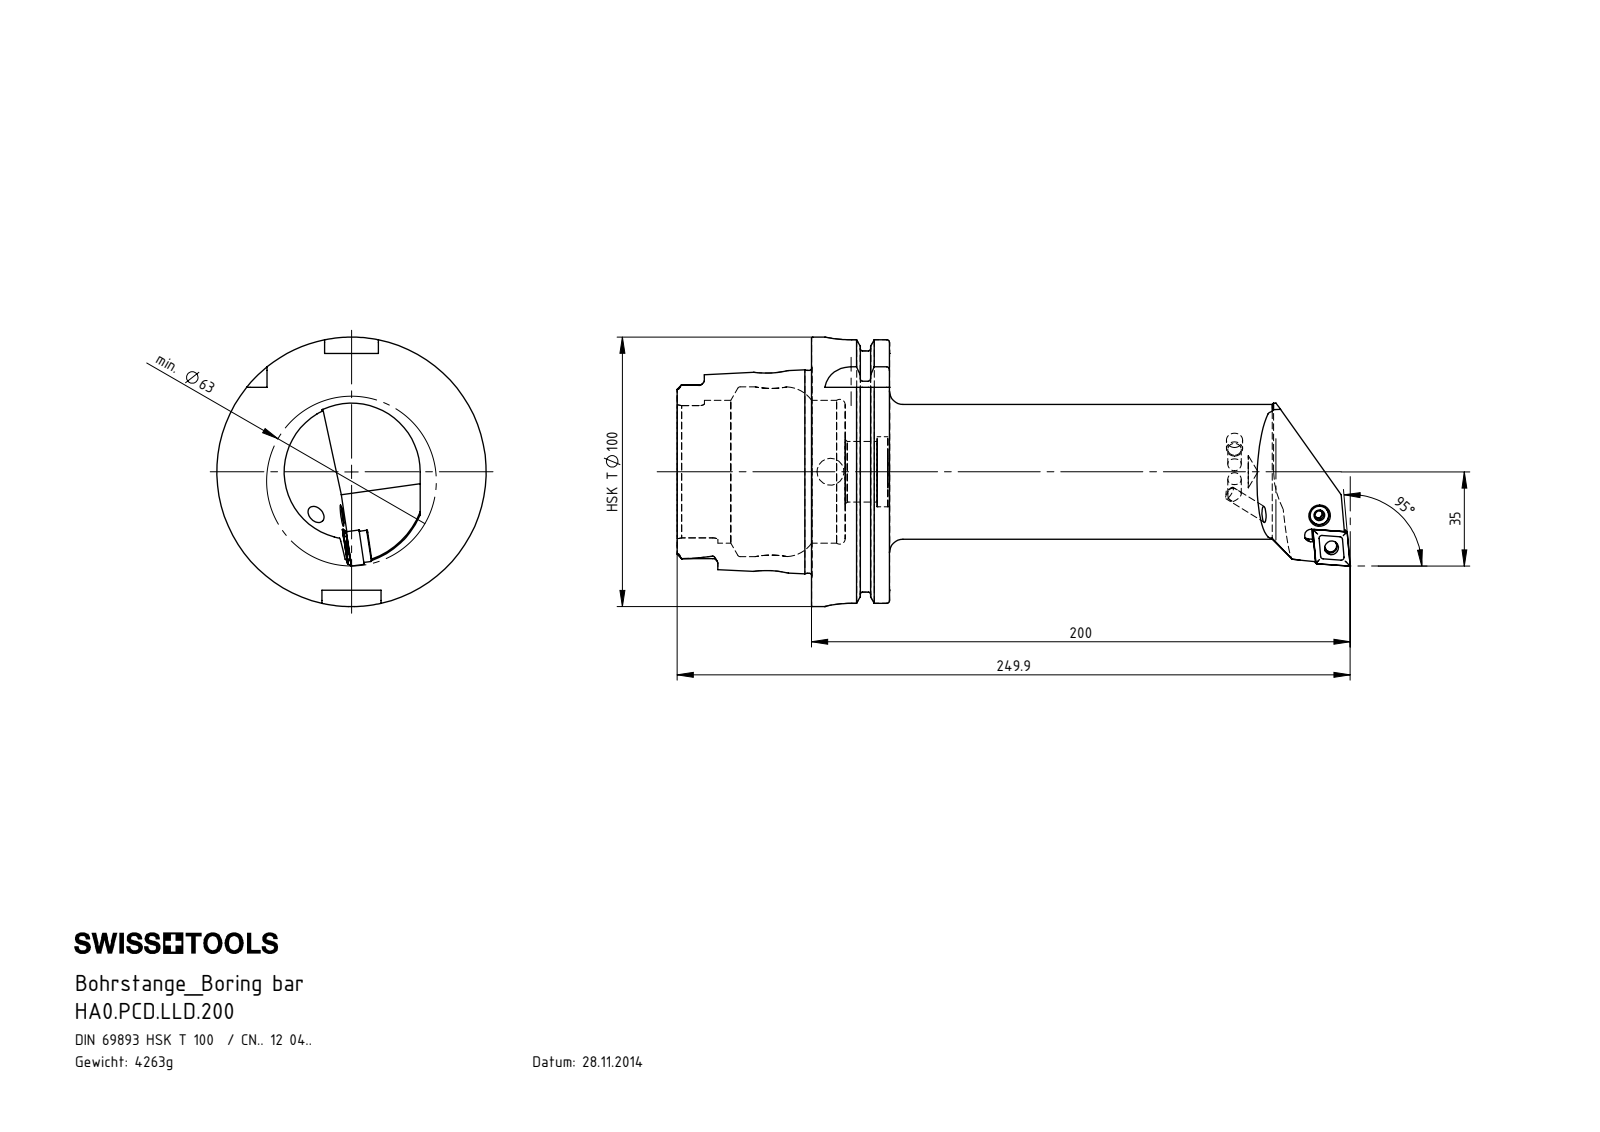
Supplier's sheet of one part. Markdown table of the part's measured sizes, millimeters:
| quantity | value |
| --- | --- |
| part name | WCD-ER3.101.000_A; WCD-ER2.101.003_A; CNMG120404; KVT_MB_600_060 (+4 more) |
| STEP written by | SolidWorks 2017 (AUTOMOTIVE_DESIGN) |
| units | millimeters |
| bodies | 8 solids, 292 faces (114 planar, 72 cylindrical, 106 other) |
| overall size | 249.86 × 100 × 100 |
| volume | 542 161 mm³ |
| surface area | 83 561 mm² |
| round holes (diameter × count) | 5 × 3, 12 × 2, 5.16 × 1, 6 × 1, 6.4 × 1, 7 × 1, 8.4 × 1, 10 × 1, 22.5 × 1, 26 × 1, 53 × 1, 63 × 1 |
| round bosses / shafts (diameter × count) | 100 × 1, 91.95 × 1, 75.26 × 1, 50 × 1, 8 × 1, 7.9 × 1, 6.4 × 1, 6 × 1 |
| partial cylindrical surfaces (radius × count) | 1.9 × 6, 0.4 × 4, 1 × 4, 10 × 4, 2.5 × 2, 4.83 × 2, 4.88 × 2, 2.1 × 1 |
| main face-to-face distances | 28.95, 12.45, 16.5, 49.9, 62.35, 78.85, 87.8, 78.2, 28.3, 15.85 |
| hole center spacings | 12.8, 12.87 |
